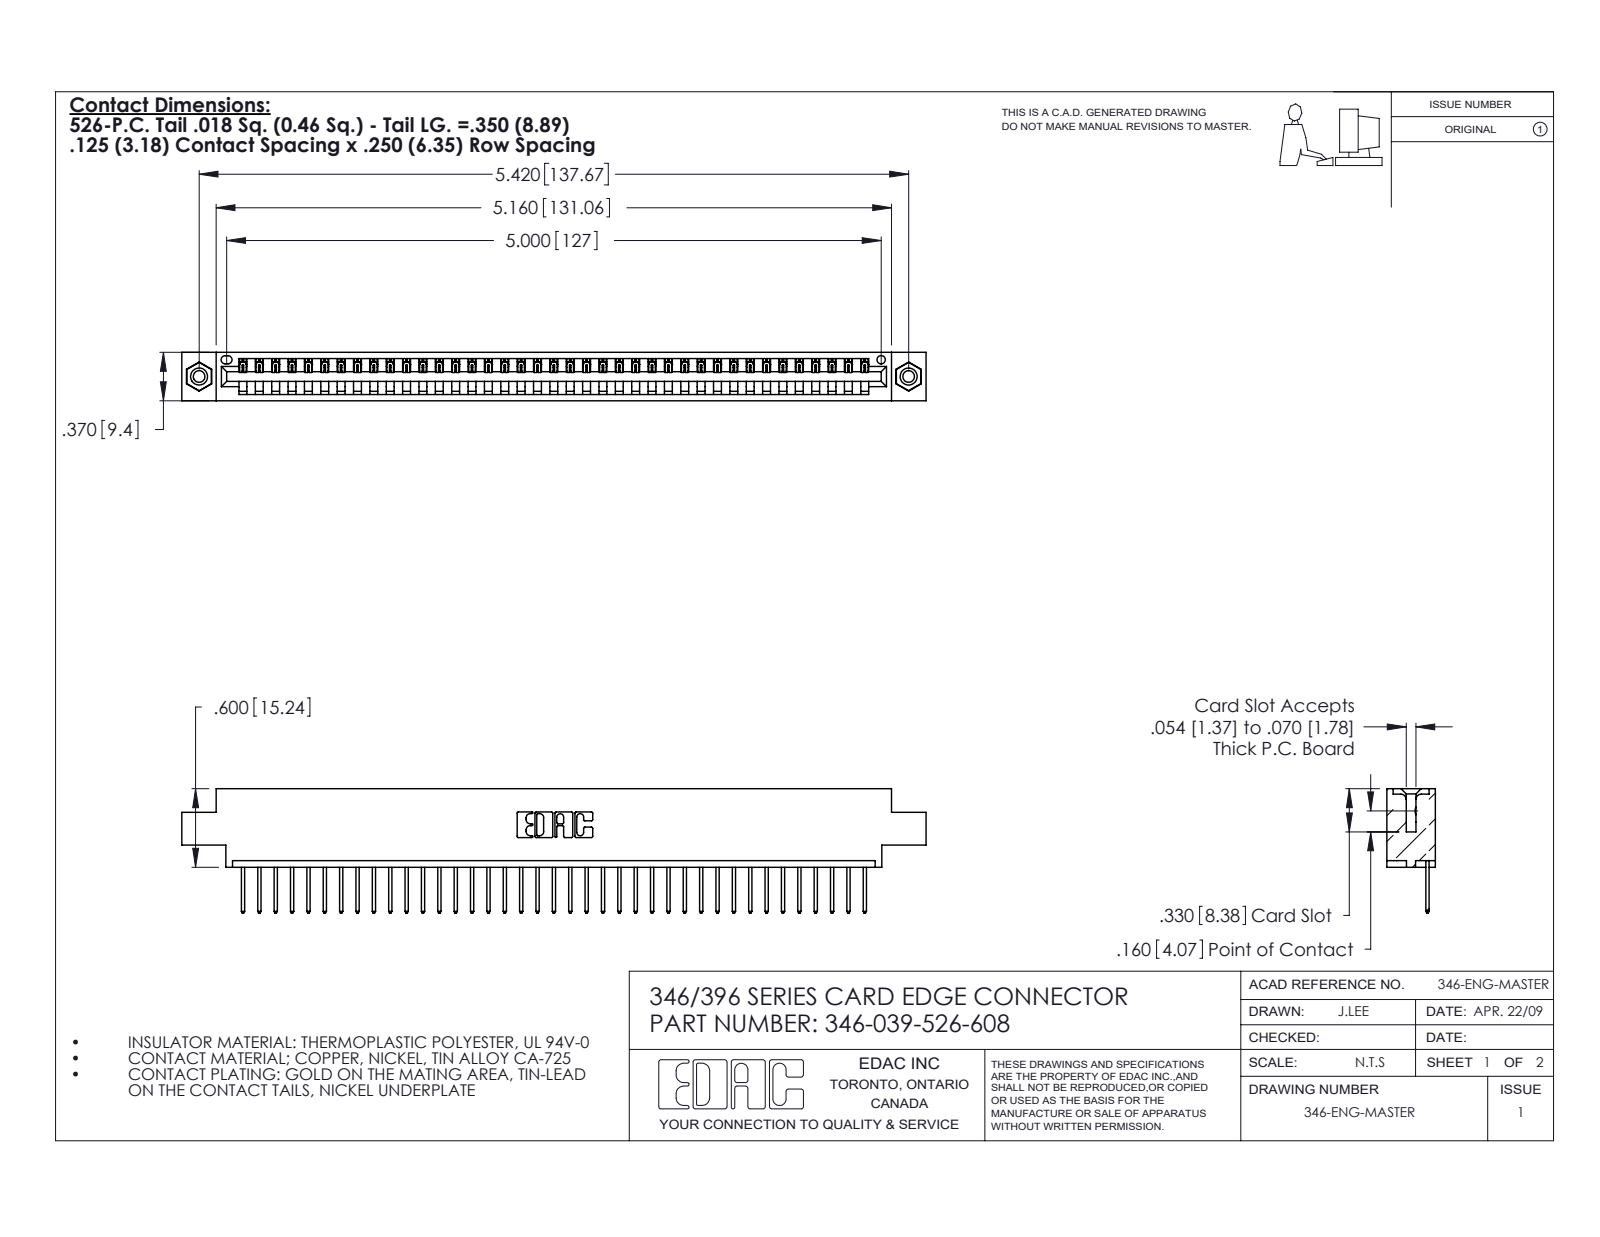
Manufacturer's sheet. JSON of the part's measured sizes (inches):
{"part_name": "345-250-001_345-250-003-102; 346 Part_0.170 Offset - 0.156 Dia-TI; 345-292-001_345-293-126; 346-039-526-608", "step_written_by": "SolidWorks 2020 (CONFIG_CONTROL_DESIGN)", "units": "inches", "bodies": {"solids": 42, "faces": 2448, "planar": 1672, "cylindrical": 760, "other": 16}, "overall_size": [5.685, 0.95, 0.37], "volume_in3": 0.83, "surface_area_in2": 26.54, "round_holes": [[0.089, 2], [0.125, 2], [0.156, 2], [0.064, 1]], "round_bosses_or_shafts": [[0.155, 2]], "partial_cylinders_radius": [[0.006, 78], [0.01, 78], [0.01, 22], [0.007, 6], [0.031, 6], [0.026, 3], [0.031, 2], [0.04, 2]], "face_to_face_distances": [0.048, 0.322, 0.37, 0.25, 0.072, 0.298, 0.025, 0.222, 0.148, 0.1], "hole_center_spacings": [0.246, 5.211, 5.42]}
